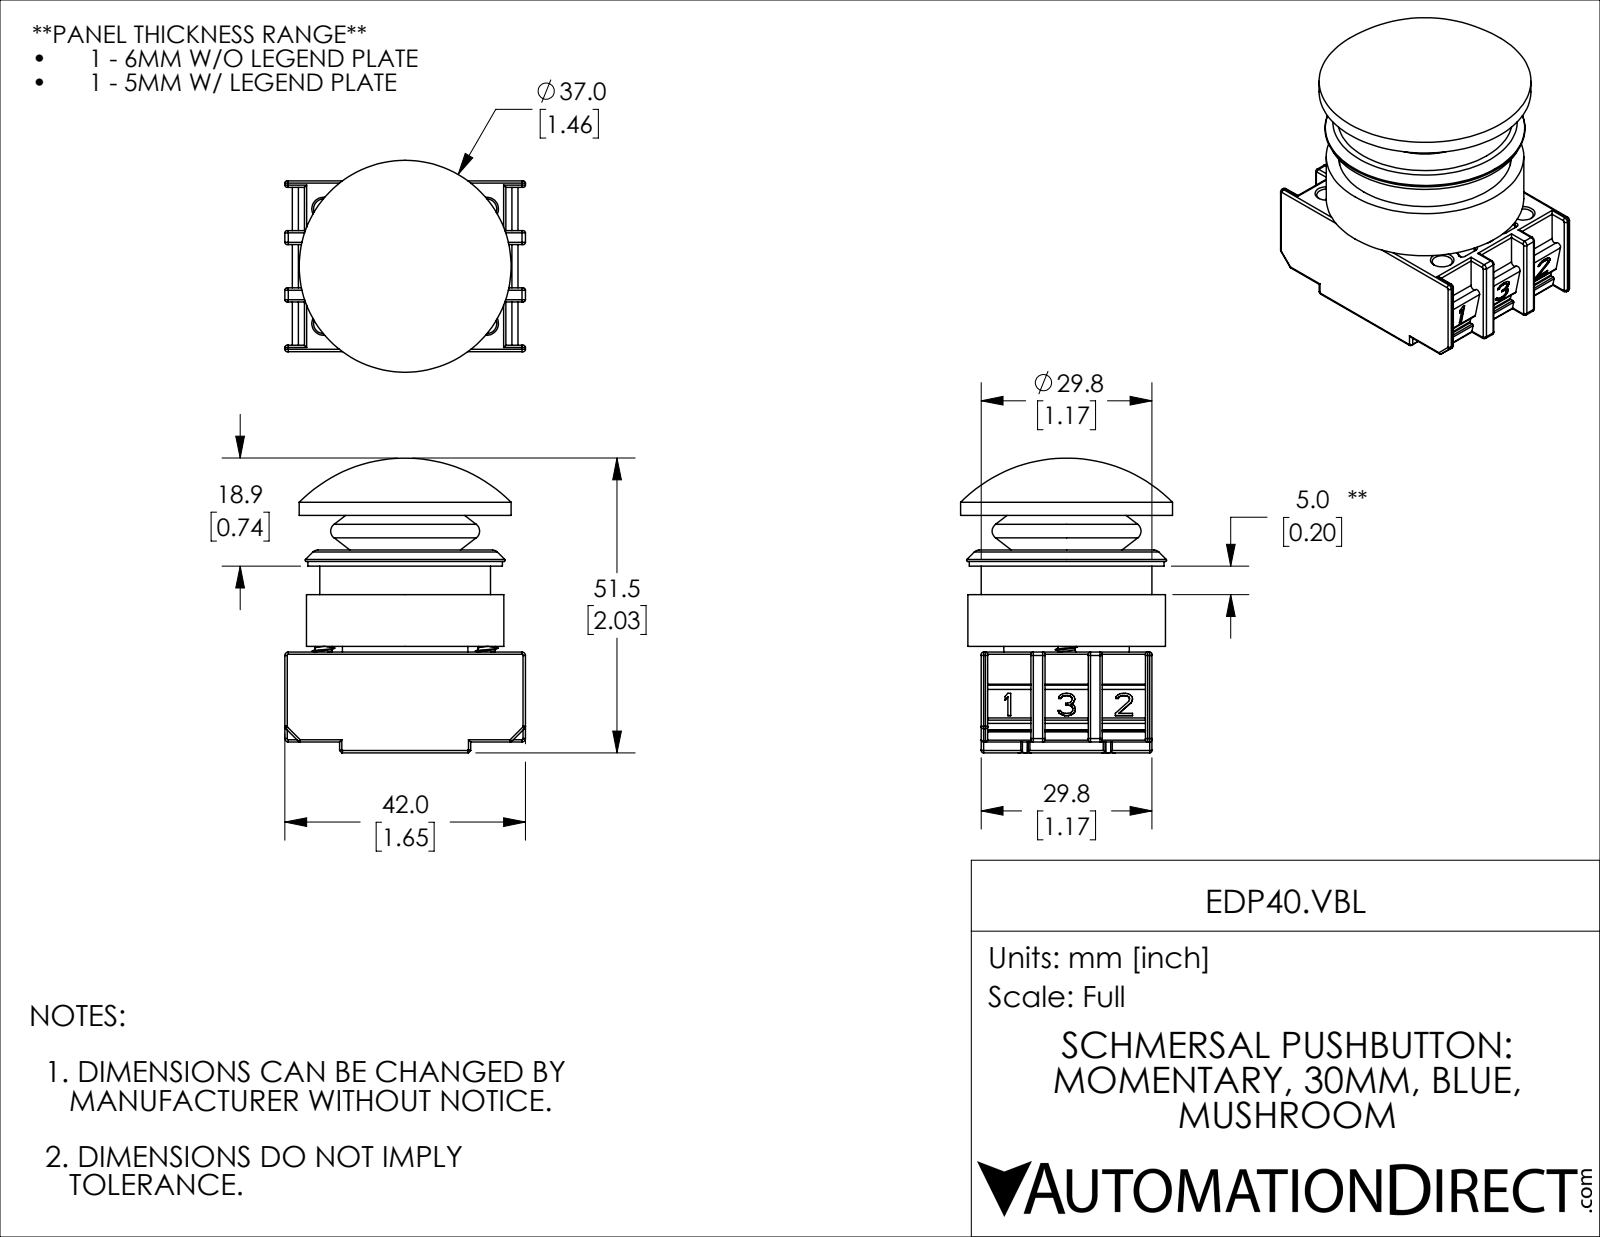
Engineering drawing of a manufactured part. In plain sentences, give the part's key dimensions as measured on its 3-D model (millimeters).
The part is named "EDP40.VBL". Its 3-D file was written by "SolidWorks 2019 (CONFIG_CONTROL_DESIGN)". It is 5 solids with 1490 faces: 538 planar, 503 cylindrical and 449 other. Overall it measures 51.45 by 42 by 37 millimeters. Its volume is 32 755 cubic millimeters and its surface area 23 609 square millimeters. Round holes: 6 of diameter 3.5, 6 of diameter 5.15, 1 of diameter 8.25, 1 of diameter 12.15, 1 of diameter 18.8, 1 of diameter 19.5, 1 of diameter 24.1, 1 of diameter 24.2, 1 of diameter 26, 1 of diameter 30.2, 1 of diameter 32. Round bosses or shafts: 2 of diameter 4.8, 2 of diameter 2.93, 1 of diameter 37, 1 of diameter 34.5, 1 of diameter 34, 1 of diameter 29.8, 1 of diameter 25.5, 1 of diameter 24. Partial cylindrical surfaces (rounded edges, fillets, slot ends): 112 of radius 0.4, 48 of radius 0.3, 28 of radius 0.2, 8 of radius 0.6, 6 of radius 0.5, 6 of radius 0.8, 2 of radius 0.1, 2 of radius 0.6. The main face-to-face distances are 18.6, 29.8, 1, 1.9, 16.8, 17.6, 35.4, 17.8, 20.95, 10. The hole center spacings are 10, 17.41, 30.2, 28.5, 14.25, 20, 34.82.
